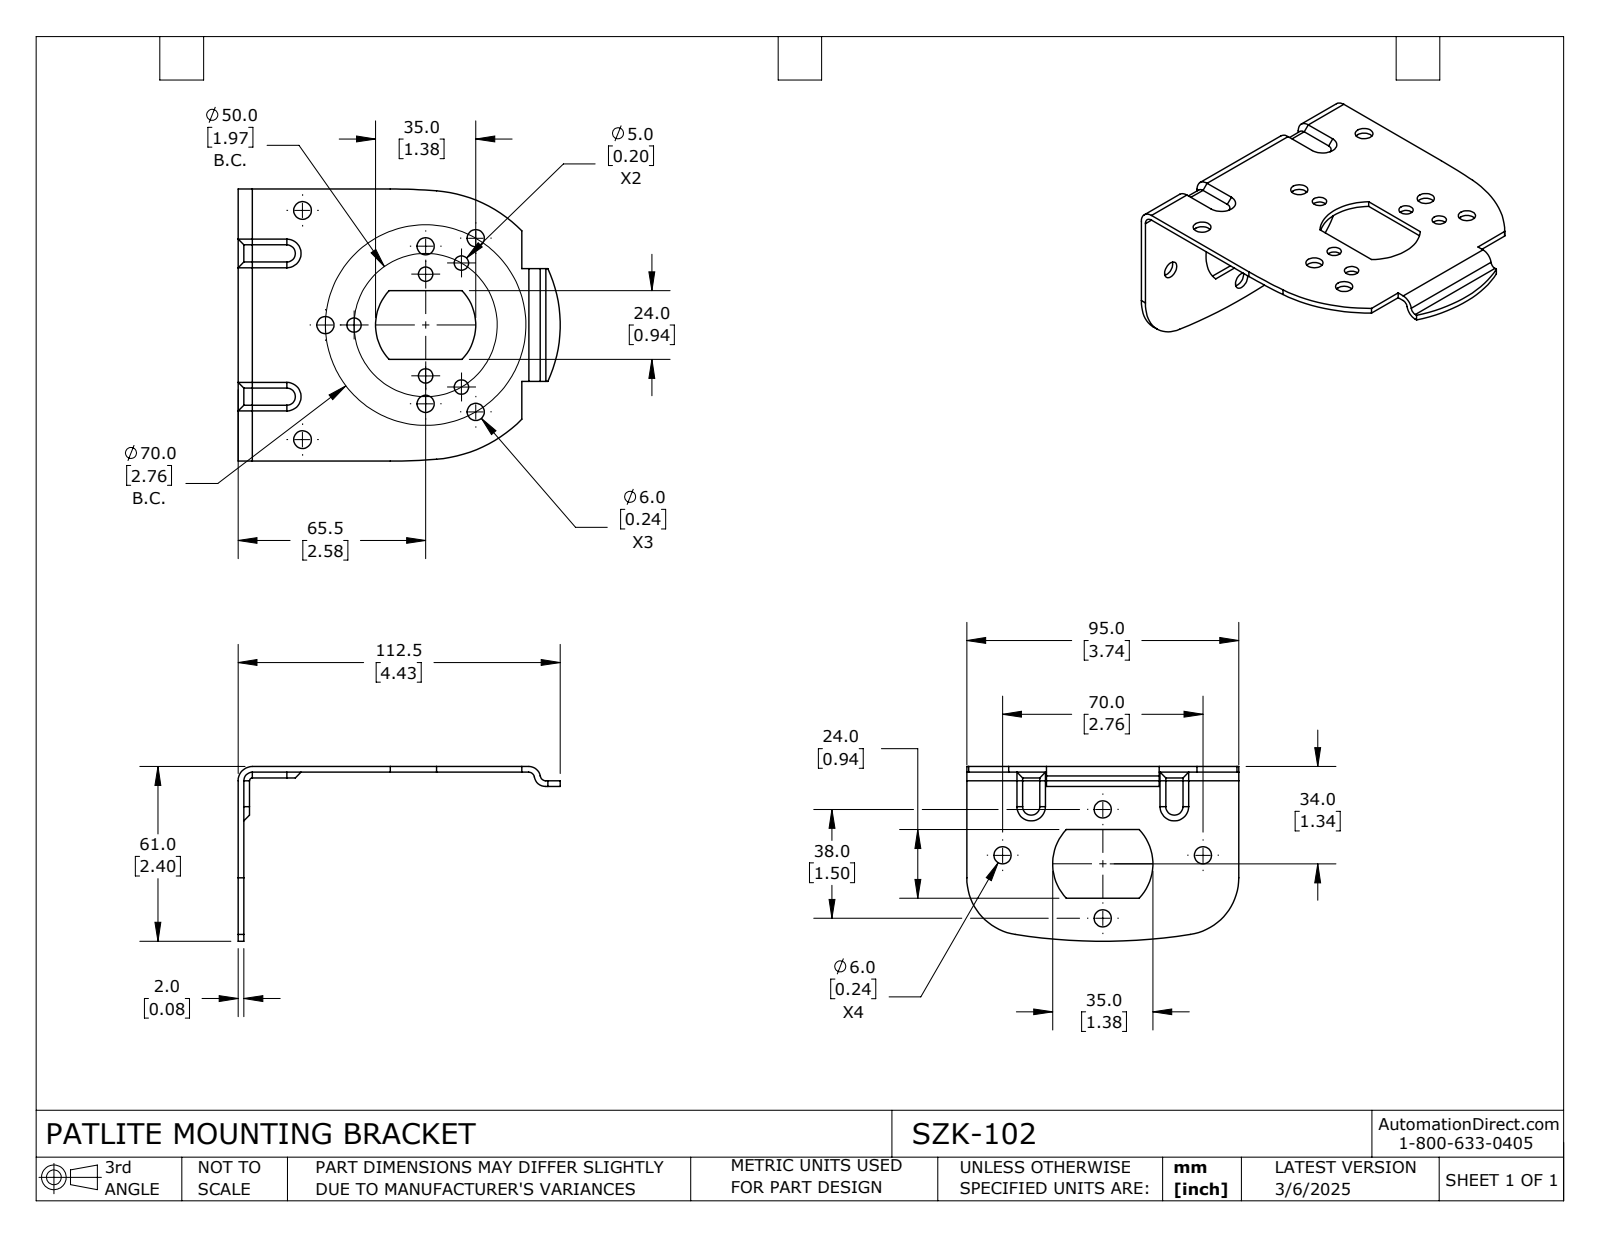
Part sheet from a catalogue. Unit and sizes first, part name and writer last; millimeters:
Units: millimetres
Overall size (bounding box): 112.5 × 95 × 61
Round holes (diameter × count): ⌀6 ×9, ⌀5 ×5, ⌀6.2 ×2
Partial cylindrical surfaces — rounded edges, fillets, slot ends (radius × count): R200 ×3, R2 ×2, R4 ×2, R17.5 ×2, R20 ×2, R1 ×1, R3 ×1, R5 ×1
Main face-to-face distances: 2, 4, 3, 5, 35.35, 95, 7, 1, 1.41, 24
Hole centre spacings: 52.2, 41.34, 10, 43.3, 60.62, 9.75, 13.09, 13.8
Volume: 25 626 mm³ · Surface area: 27 822 mm²
Bodies: 1 solid, 116 faces (40 planar, 60 cylindrical, 16 other)
Part name (STEP PRODUCT): SZK-102
STEP written by: SolidWorks 2024 (CONFIG_CONTROL_DESIGN)
